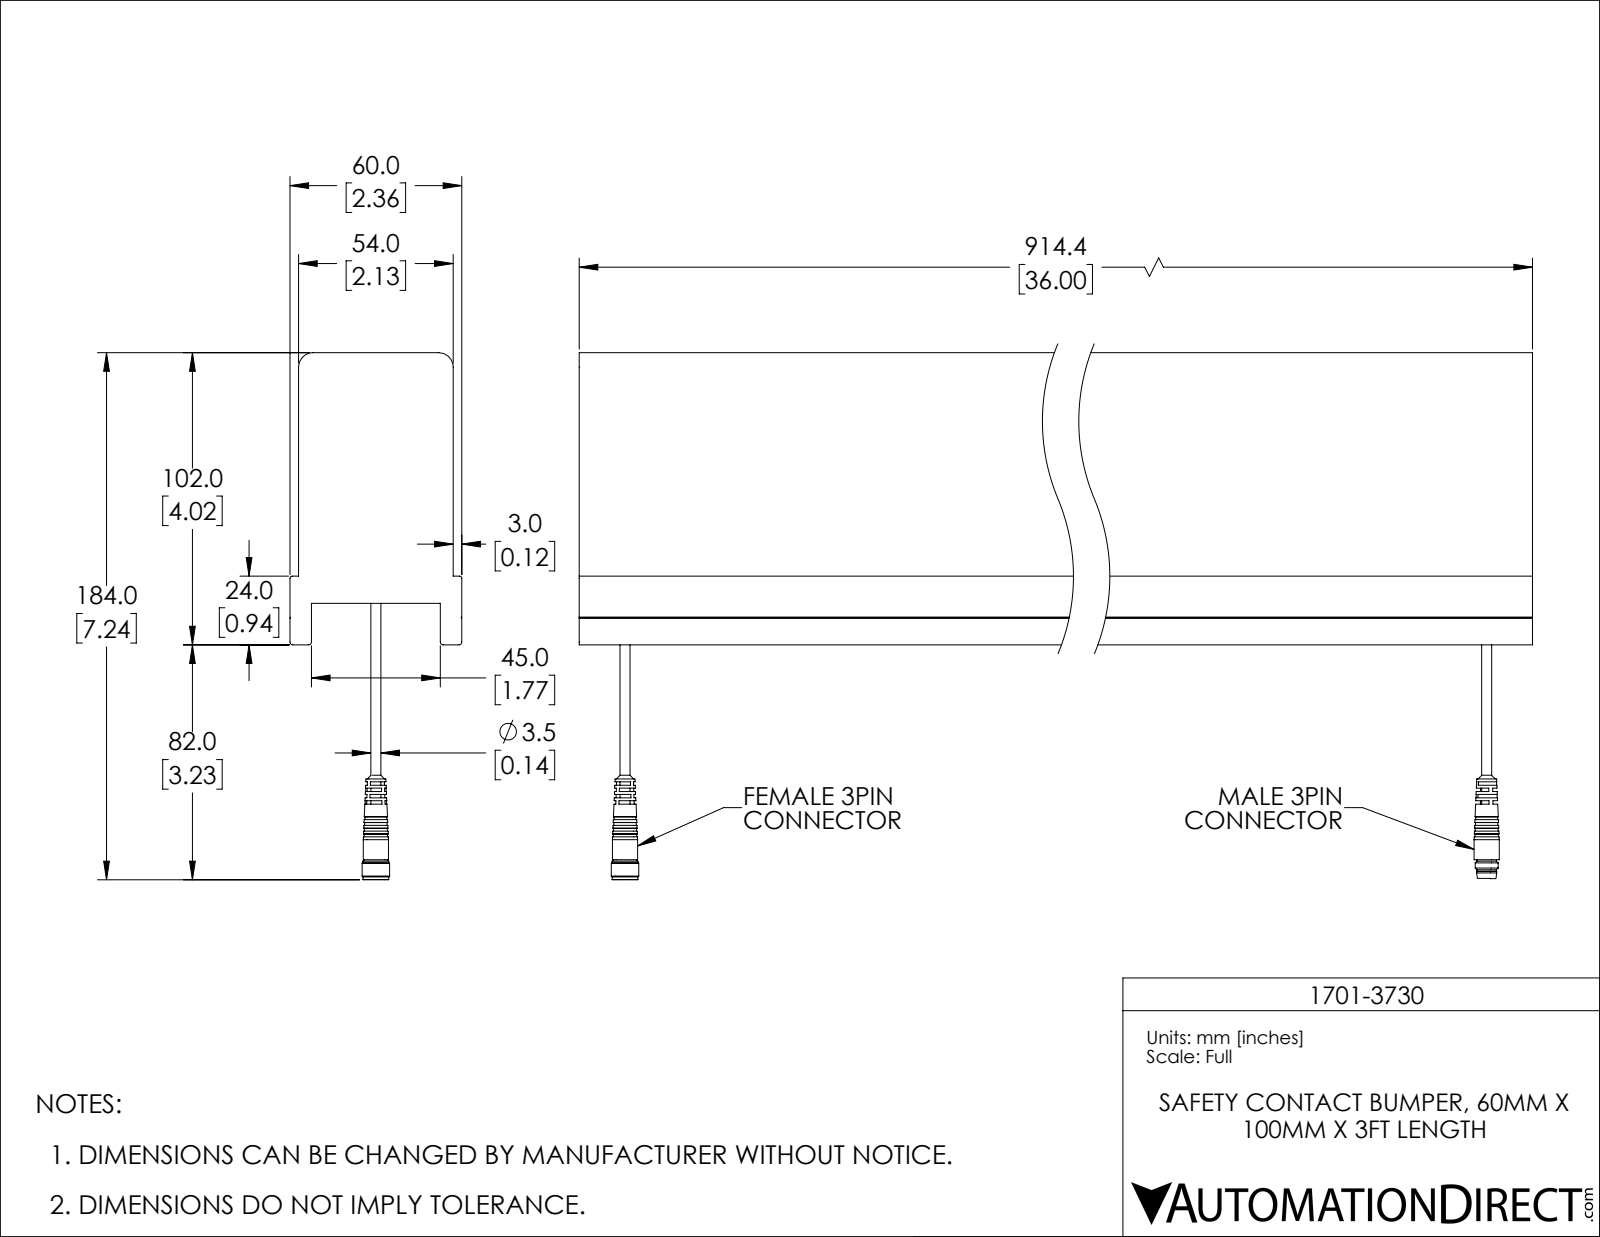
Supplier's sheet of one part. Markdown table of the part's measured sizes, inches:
| quantity | value |
| --- | --- |
| part name | 1701-3730 |
| STEP written by | SolidWorks 2018 (AUTOMOTIVE_DESIGN) |
| units | inches |
| bodies | 20 solids, 294 faces (138 planar, 59 cylindrical, 97 other) |
| overall size | 36 × 7.244 × 2.362 |
| volume | 278.6 in³ |
| surface area | 515.3 in² |
| round holes (diameter × count) | 0.063 × 3, 0.134 × 2, 0.228 × 1, 0.232 × 1, 0.272 × 1, 0.283 × 1 |
| round bosses / shafts (diameter × count) | 0.047 × 16, 0.031 × 4, 0.039 × 3, 0.346 × 2, 0.138 × 2, 0.378 × 1, 0.354 × 1, 0.315 × 1 |
| main face-to-face distances | 2.126, 3.445, 0.118, 2.244, 0.295, 2.067, 0.177, 1.949, 2.362, 1.772 |
| hole center spacings | 0.069, 0.098, 34.789, 0.138, 34.691, 34.74 |
